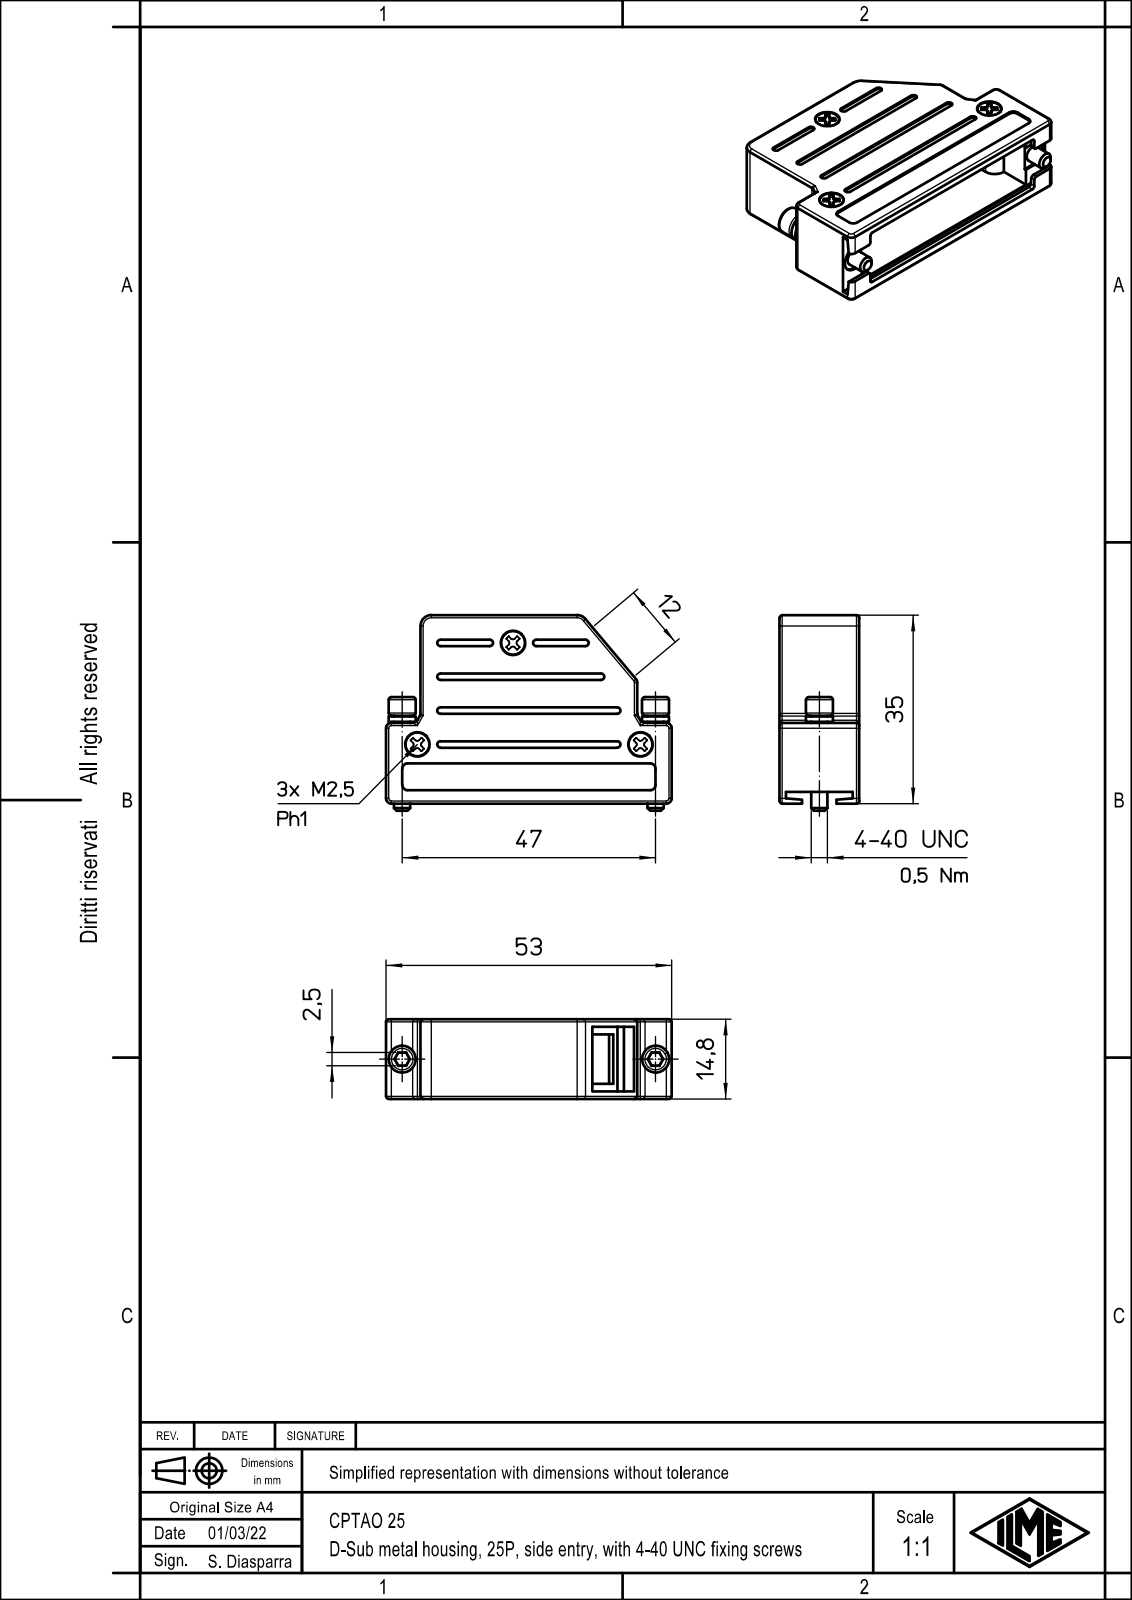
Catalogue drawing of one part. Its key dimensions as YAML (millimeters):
part_name: "CPTAO_25"
step_written_by: "Creo Elements/Direct Modeling 20.1B 02-Apr-2019 (C) Parametric Technology GmbH (AUTOMOTIVE_DESIGN)"
units: millimeters
bodies: {solids: 1, faces: 625, planar: 158, cylindrical: 193, other: 274}
overall_size: [53, 36.3, 14.8]
volume: 8666
surface_area: 9214
round_bosses_or_shafts:
  - {diameter: 5, count: 2}
  - {diameter: 3, count: 2}
partial_cylinders:
  - {radius: 0.5, count: 40}
  - {radius: 1, count: 13}
  - {radius: 0.6, count: 10}
  - {radius: 2, count: 2}
  - {radius: 2.05, count: 2}
  - {radius: 2.4, count: 2}
face_to_face_distances: [13.3, 1.5, 11.8, 14.8, 1.2, 13, 13.1, 1.3, 14.3, 14.5]
